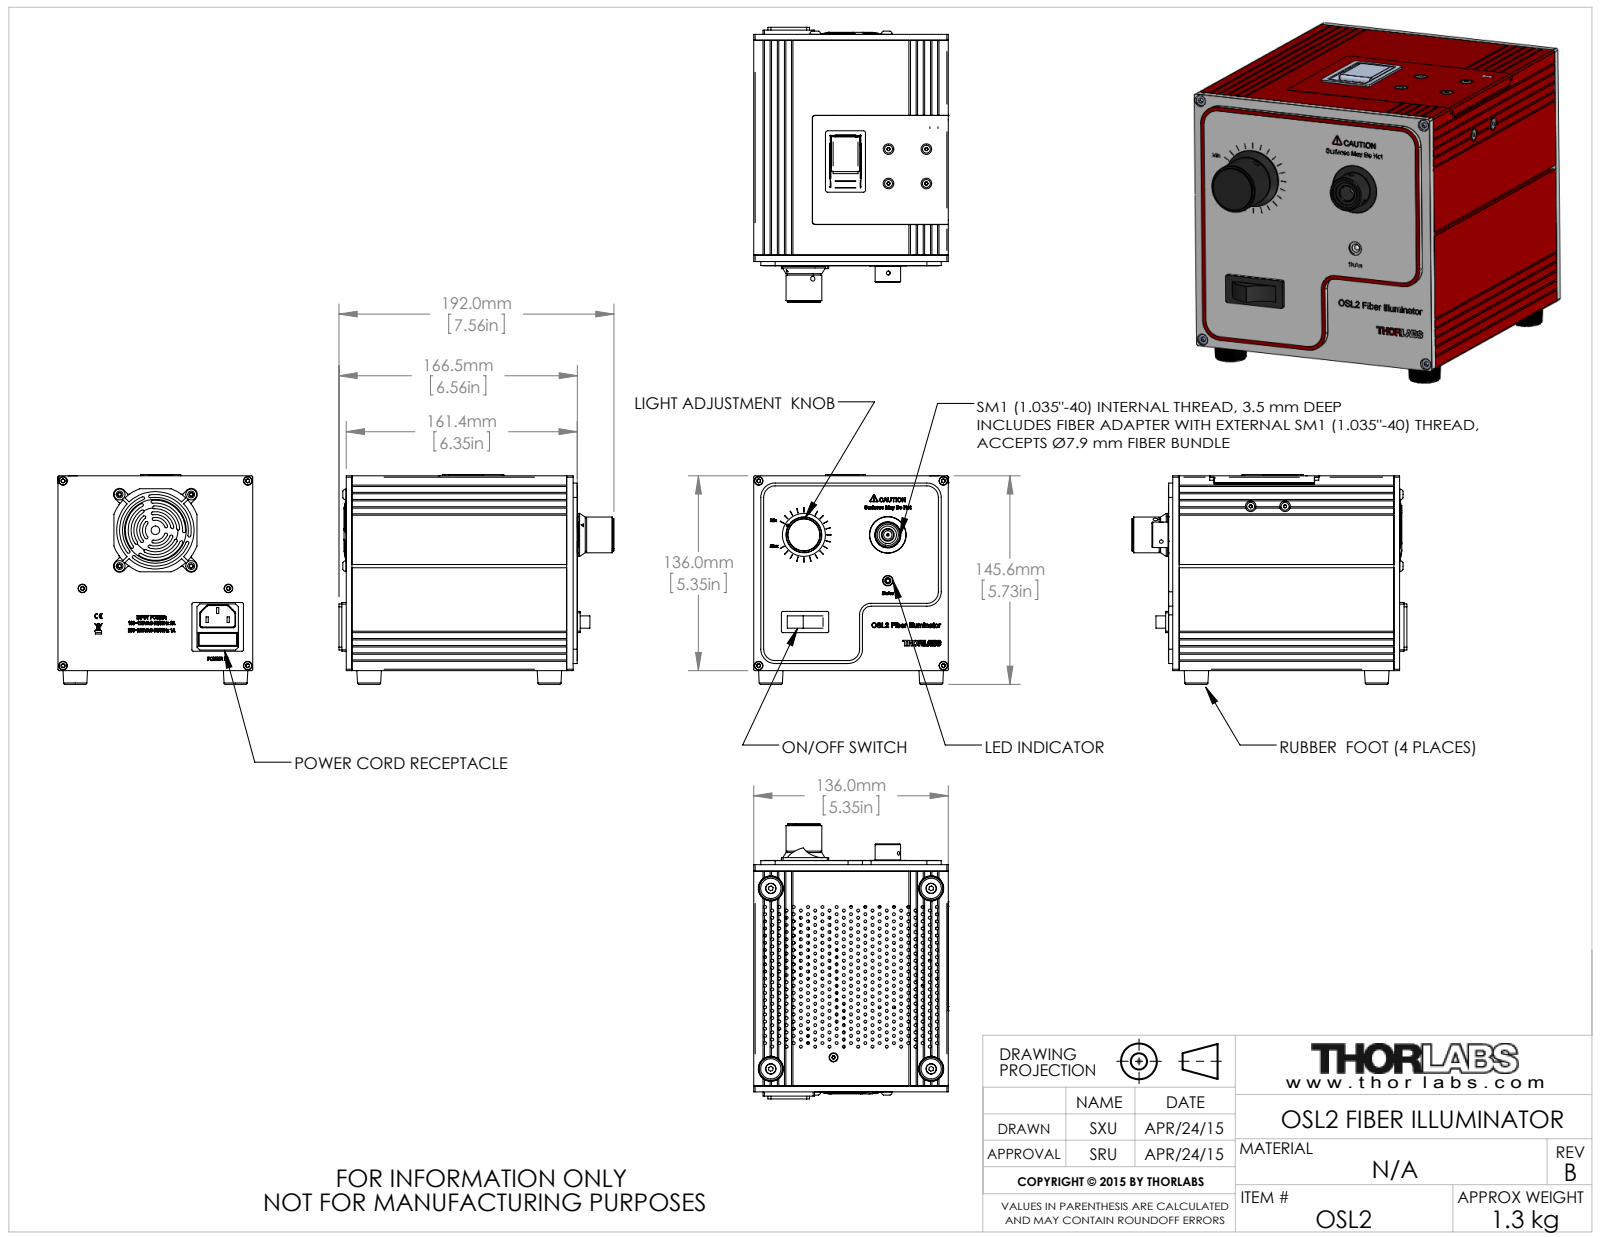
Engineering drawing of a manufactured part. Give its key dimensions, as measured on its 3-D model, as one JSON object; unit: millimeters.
{"part_name": "DB0016 M3 x 6 Skt Cap; DA0003 - M1.6 x 4 Cheese Hd.; PPSB4-10; M4 flat Washer (+8 more)", "step_written_by": "SolidWorks 2014 (CONFIG_CONTROL_DESIGN)", "units": "millimeters", "bodies": {"solids": 102, "faces": 7224, "planar": 3657, "cylindrical": 2390, "other": 1177}, "overall_size": [192, 146.52, 136], "volume_mm3": 967011, "surface_area_mm2": 543755, "round_holes": [[2.01, 260], [2, 240], [2.5, 18], [6, 8], [2.7, 6], [3.3, 6], [3.5, 6], [4.2, 6], [4.6, 6], [7.2, 5], [3.2, 4], [3.24, 4]], "round_bosses_or_shafts": [[3, 20], [5.5, 18], [4, 13], [5.54, 7], [7, 6], [5, 6], [6, 5], [8, 4]], "partial_cylinders_radius": [[1, 100], [0.5, 70], [1.75, 42], [0.3, 32], [2, 24], [0.2, 16], [0.38, 15], [1.5, 14]], "face_to_face_distances": [2, 134, 136, 132, 1.6, 64, 70, 72, 8, 62.4], "hole_center_spacings": [10, 11.18, 20.62, 30.41, 20, 40.31, 30, 50]}
